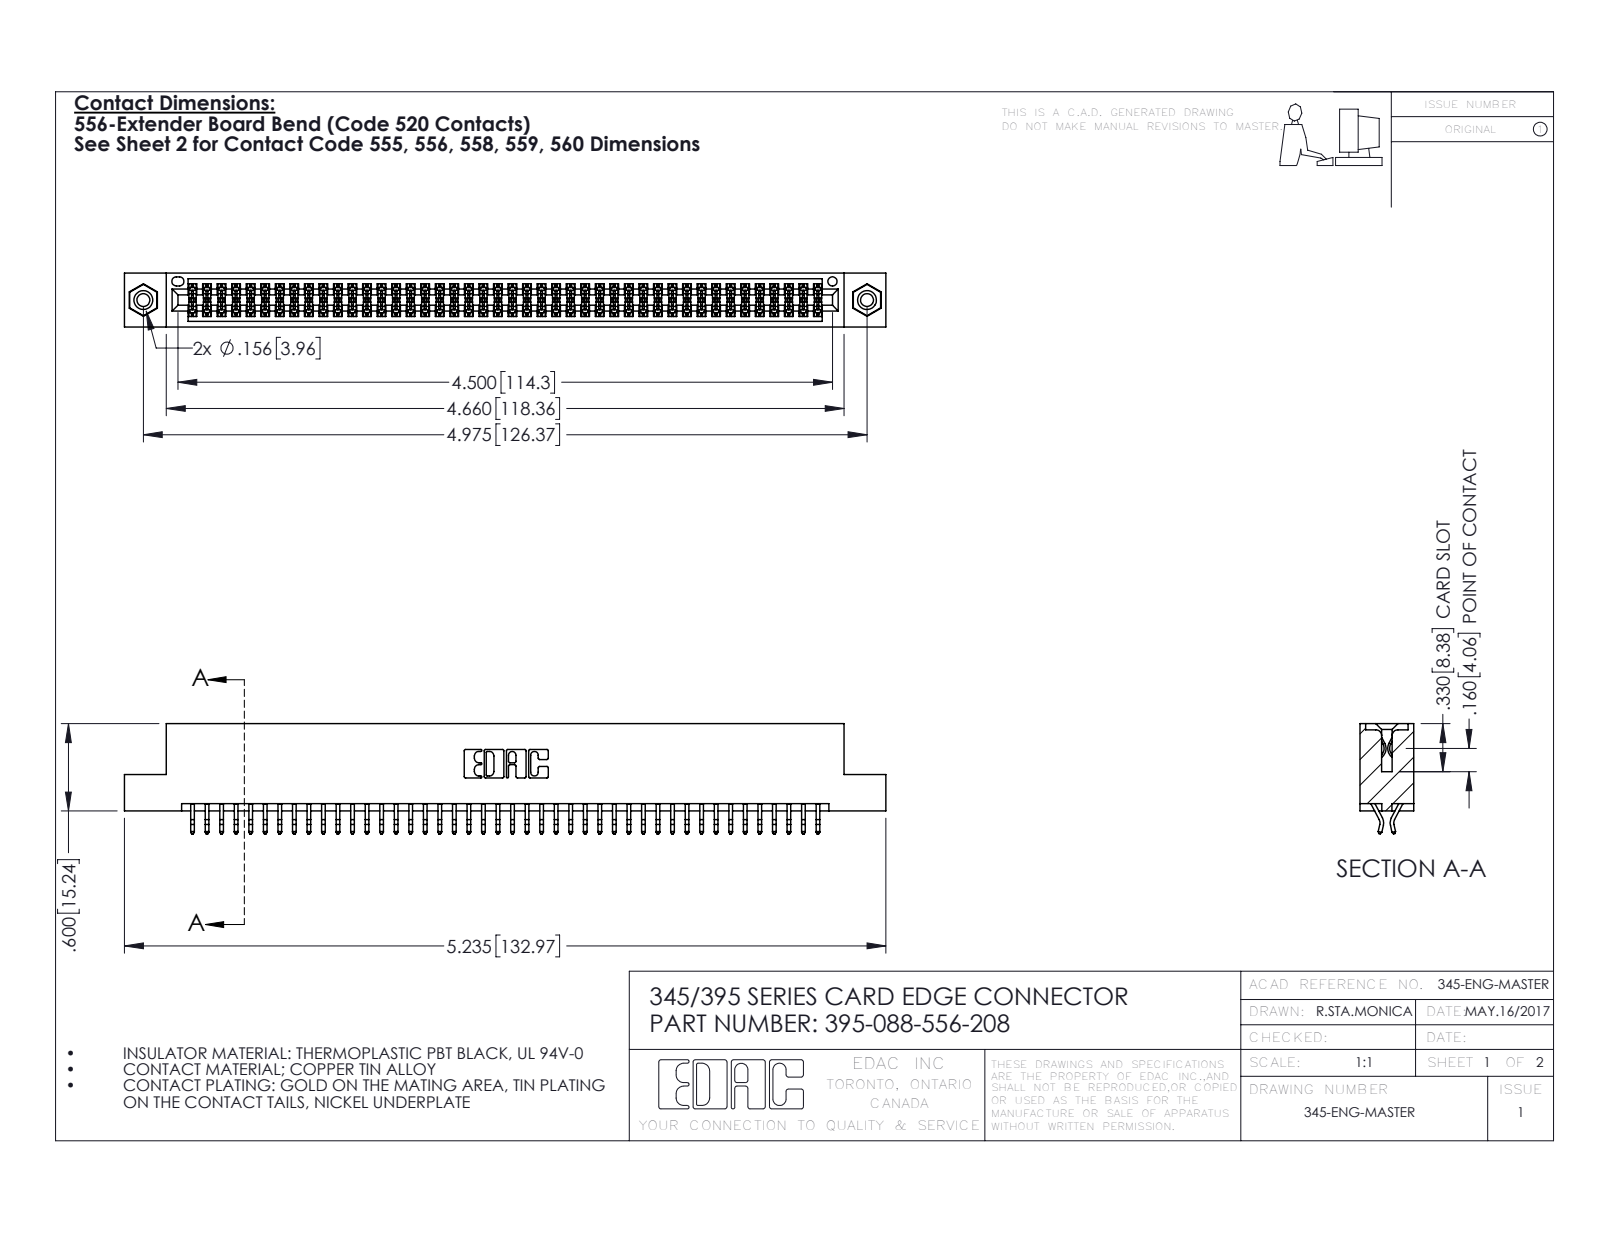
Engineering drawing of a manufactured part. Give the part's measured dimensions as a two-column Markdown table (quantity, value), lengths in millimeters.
| quantity | value |
| --- | --- |
| part name | 395-088-556-208; 345 Part_Flush Mounting Lugs - 0.156 Dia-TI; 345-292-001_556 Tail; 345-250-001_345-250-003-102 |
| STEP written by | SolidWorks 2016 (CONFIG_CONTROL_DESIGN) |
| units | millimeters |
| bodies | 91 solids, 5114 faces (3368 planar, 1730 cylindrical, 16 other) |
| overall size | 133 × 19.2 × 9.4 |
| volume | 12 900 mm³ |
| surface area | 19 080 mm² |
| round holes (diameter × count) | 2.3 × 2, 3.2 × 2, 4 × 2, 1.6 × 1 |
| round bosses / shafts (diameter × count) | 3.9 × 2 |
| partial cylindrical surfaces (radius × count) | 0.2 × 132, 0.3 × 22, 0.2 × 6, 0.8 × 6, 0.7 × 3, 0.3 × 2, 0.4 × 2, 0.5 × 2 |
| main face-to-face distances | 1.8, 7.6, 9.4, 5.1, 0.6, 2.5, 6.9, 5.7, 4.4, 3.8 |
| hole center spacings | 6.9, 120.4, 126.4 |
